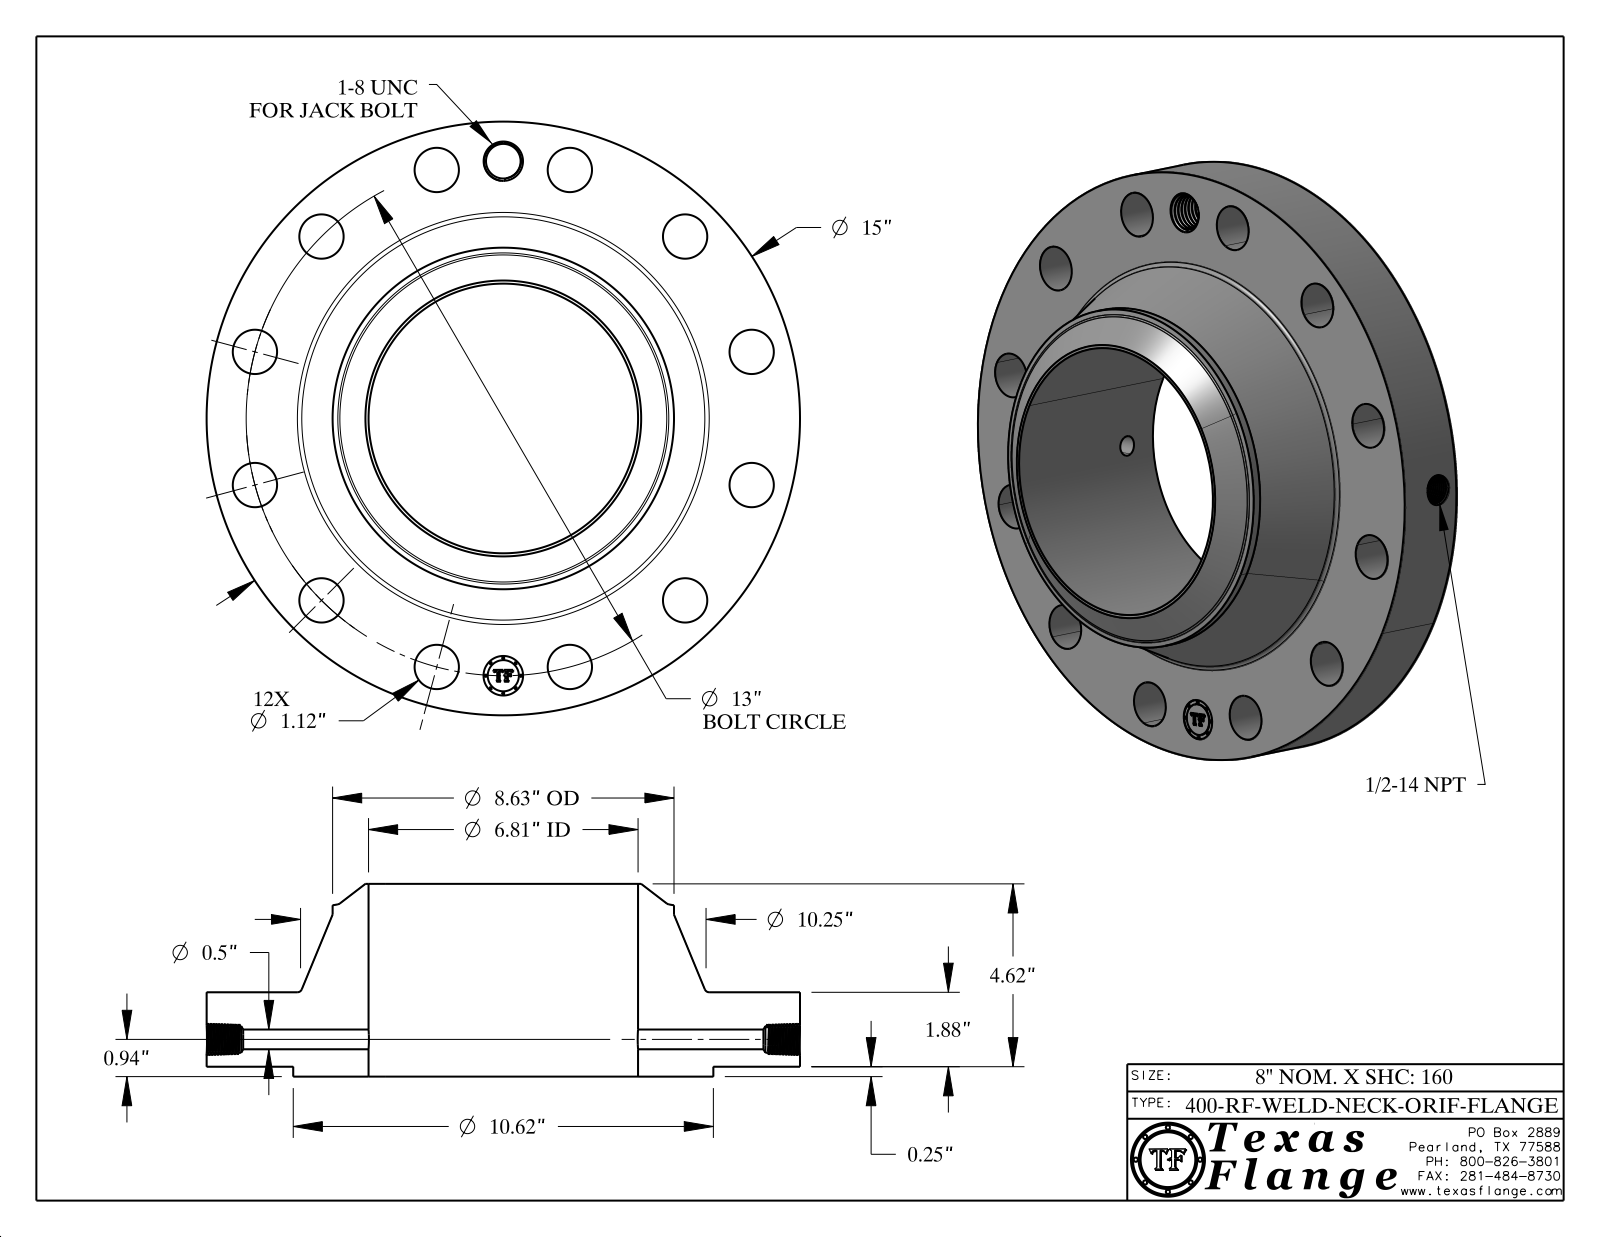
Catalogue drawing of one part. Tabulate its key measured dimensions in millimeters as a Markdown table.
| quantity | value |
| --- | --- |
| part name | 400-RF-WELD-NECK |
| STEP written by | CATIA V5 STEP AP214 (AUTOMOTIVE_DESIGN) |
| units | millimeters |
| bodies | 1 solid, 783 faces (369 planar, 101 cylindrical, 313 other) |
| overall size | 381 × 381 × 123.7 |
| volume | 5 375 000 mm³ |
| surface area | 393 000 mm² |
| round holes (diameter × count) | 28.4 × 12, 12.7 × 1, 17.1 × 1, 22.2 × 1, 25.4 × 1, 173.1 × 1 |
| round bosses / shafts (diameter × count) | 1.5 × 8, 381 × 1, 269.7 × 1, 219.2 × 1, 20 × 1 |
| main face-to-face distances | 47.8, 6.4, 54.1, 123.7, 117.3, 69.6, 53.7, 47.4, 0.4, 70 |
| hole center spacings | 165.1, 85.5, 233.5, 286, 318.9, 330.2, 43.1, 126.4 |
